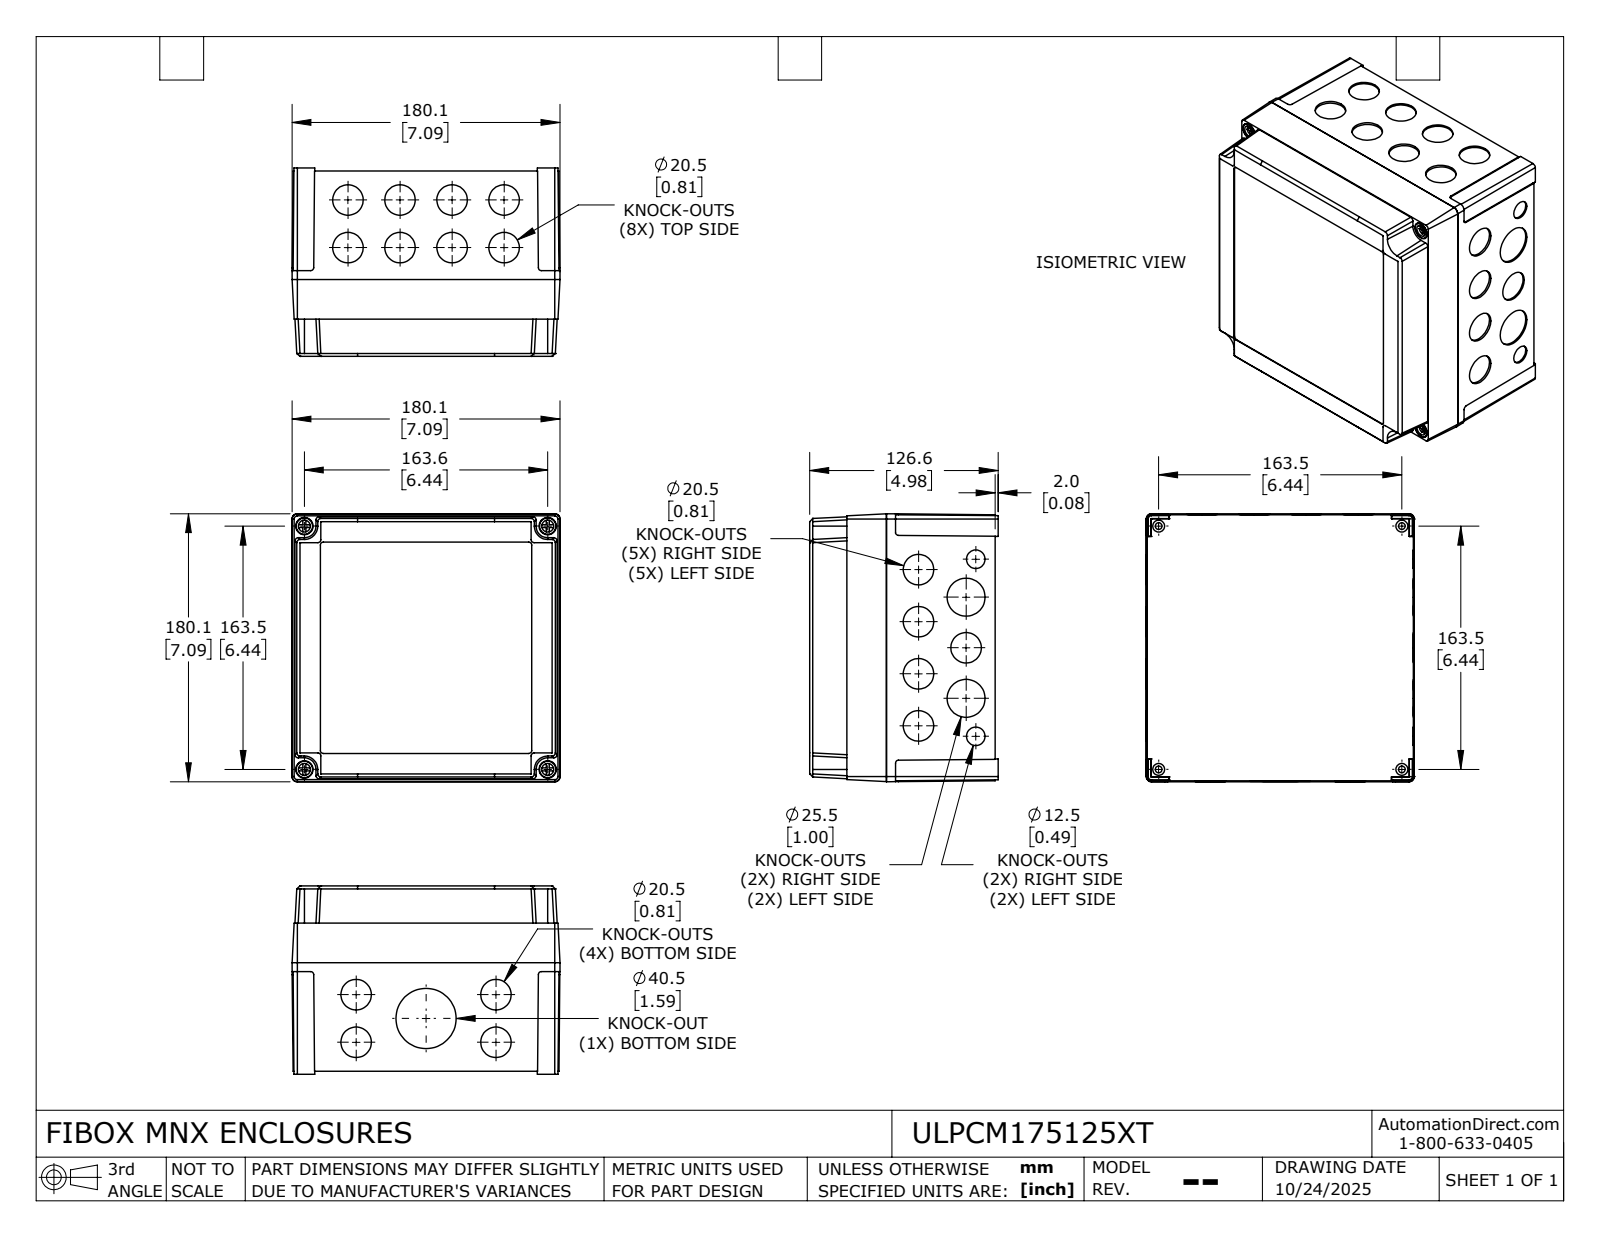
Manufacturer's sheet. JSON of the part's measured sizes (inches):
{"part_name": "ULPCM175125XT_Default", "step_written_by": "SolidWorks 2024 (CONFIG_CONTROL_DESIGN)", "units": "inches", "bodies": {"solids": 12, "faces": 544, "planar": 358, "cylindrical": 136, "other": 50}, "overall_size": [7.091, 7.091, 4.984], "volume_in3": 28.96, "surface_area_in2": 490.2, "round_holes": [[0.807, 17], [0.126, 12], [0.157, 12], [0.315, 8], [0.177, 4], [0.457, 4], [0.492, 2], [1.004, 2], [1.594, 1]], "round_bosses_or_shafts": [[0.315, 12], [0.098, 8], [0.433, 4], [0.283, 4]], "partial_cylinders_radius": [[0.079, 8], [0.083, 8], [0.197, 4]], "face_to_face_distances": [0.165, 4.807, 0.118, 4.689, 0.079, 4.886, 4.768, 0.077, 0.055, 0.022], "hole_center_spacings": [6.437, 1.378, 1.333, 1.969, 2.866, 3.252, 4.79, 5.207]}
